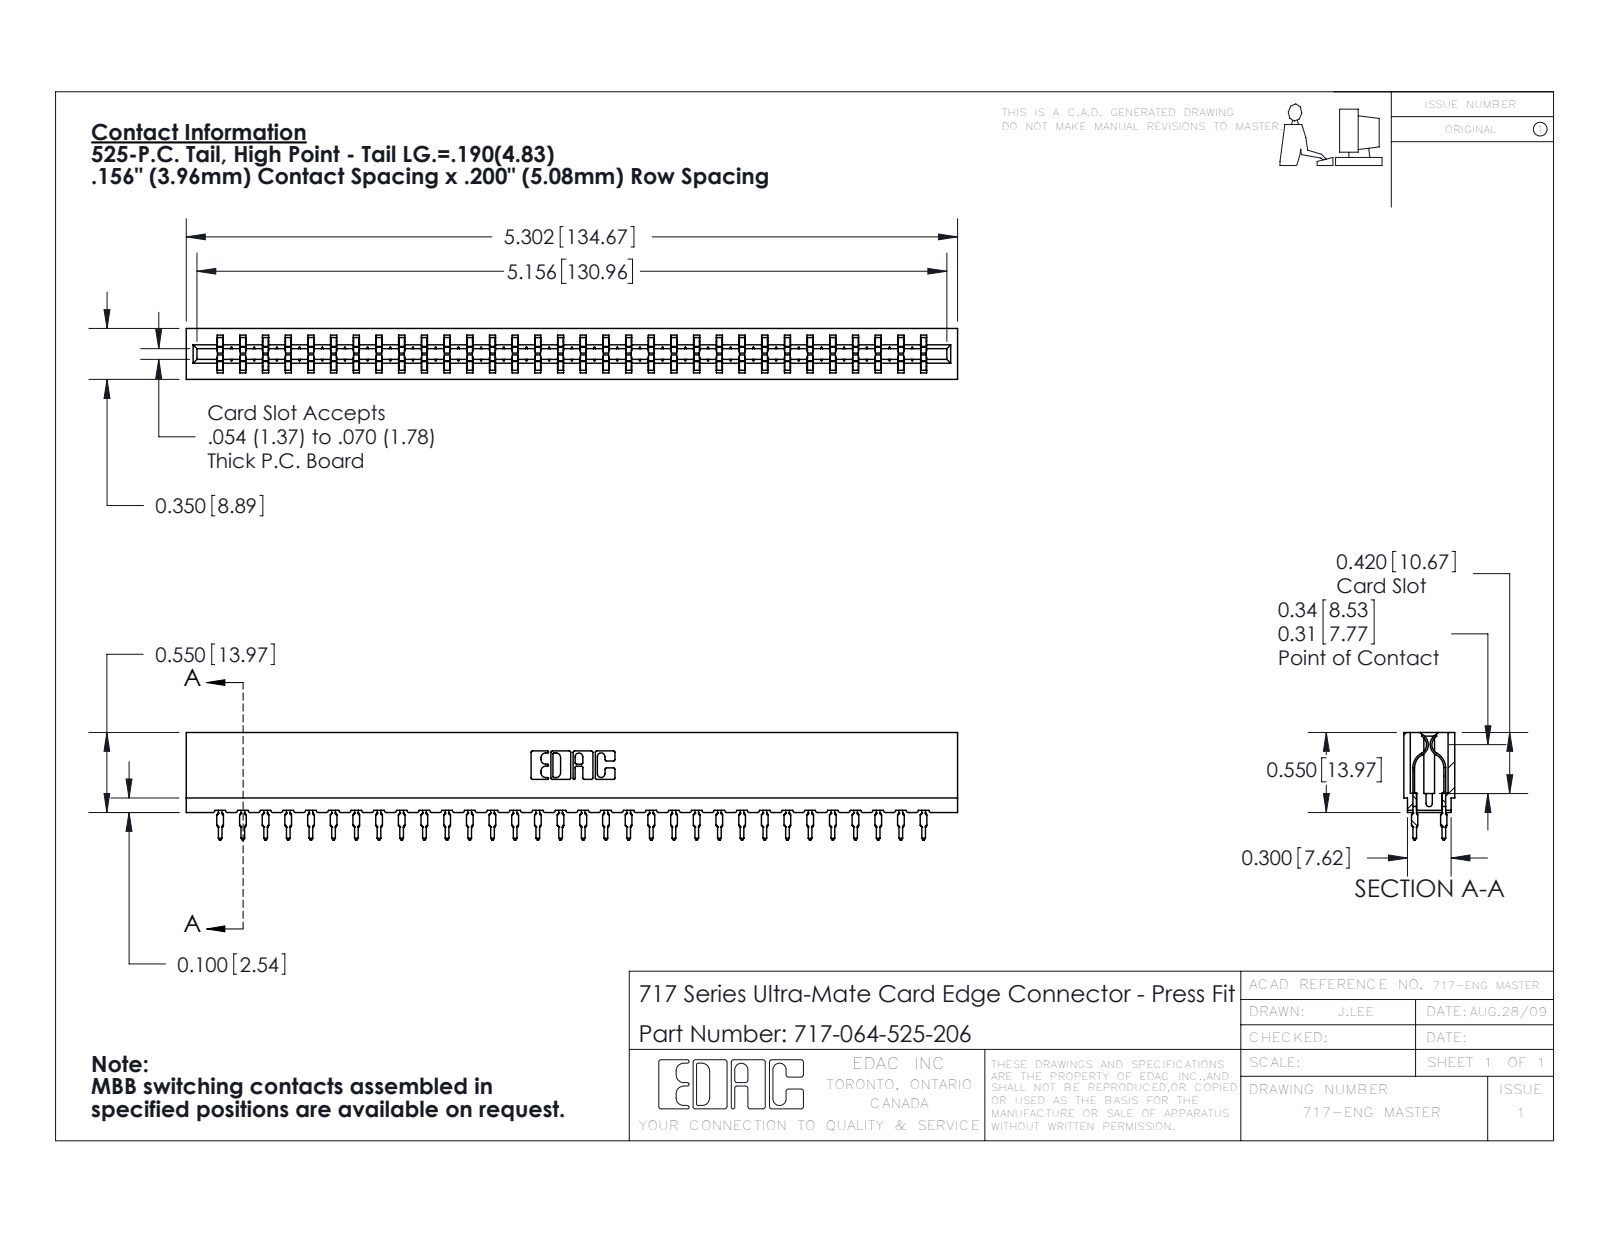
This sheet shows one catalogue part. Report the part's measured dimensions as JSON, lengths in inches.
{"part_name": "717-064-525-206; 745-292-001_525; 717 Part_Insulator Option - 06", "step_written_by": "SolidWorks 2016 (CONFIG_CONTROL_DESIGN)", "units": "inches", "bodies": {"solids": 65, "faces": 5854, "planar": 3030, "cylindrical": 1160, "other": 1664}, "overall_size": [5.302, 0.739, 0.35], "volume_in3": 0.714, "surface_area_in2": 27.41, "partial_cylinders_radius": [[0.021, 128], [0.015, 64], [0.01, 22], [0.005, 8], [0.011, 8], [0.007, 6], [0.031, 6], [0.026, 3]], "face_to_face_distances": [0.212, 0.138, 0.35, 0.063, 0.287, 0.076, 0.149, 0.074, 0.045, 0.305]}
